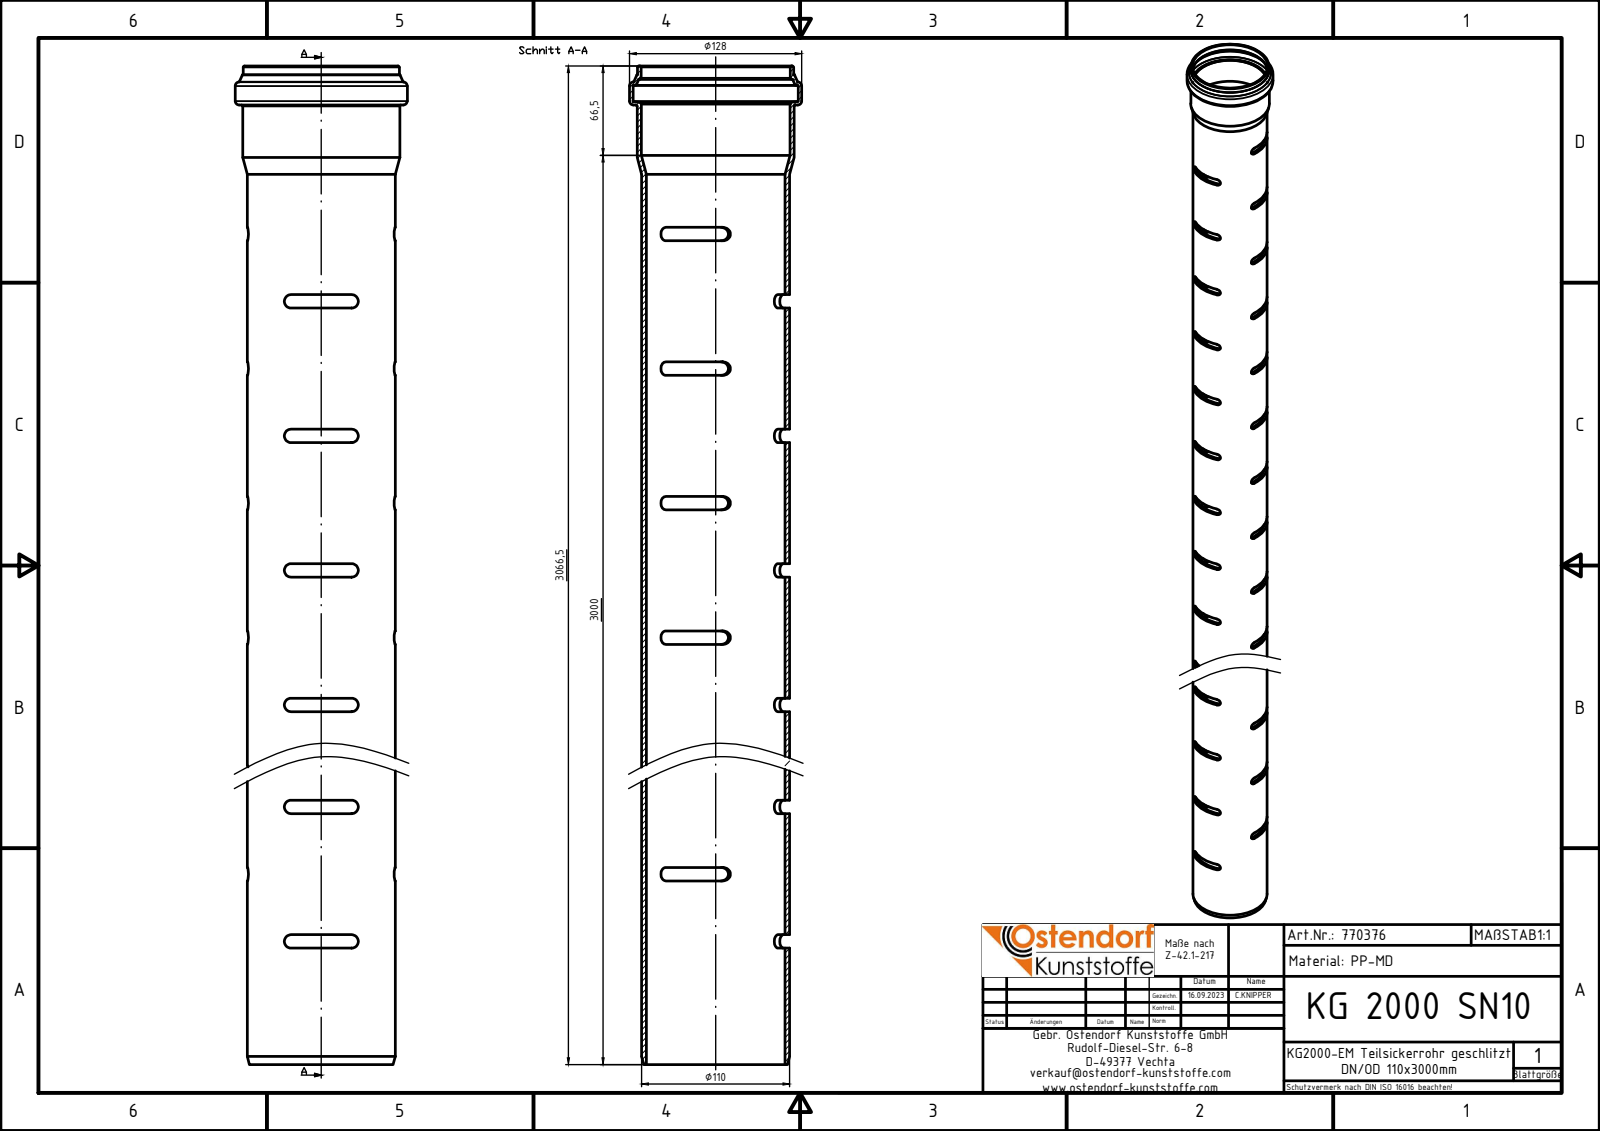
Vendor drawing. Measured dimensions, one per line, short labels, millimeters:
name: 770376z
written by: Autodesk Inventor 2024 (AUTOMOTIVE_DESIGN)
unit: mm
bodies: 1 solid, 384 faces (179 planar, 183 cylindrical, 22 other)
size: 3066.5 × 128 × 128
volume: 3 440 000 mm³; area: 2 007 000 mm²
holes: 1× ⌀102.96, 1× ⌀110.5, 1× ⌀110.9, 1× ⌀122.8
bosses: 1× ⌀128, 1× ⌀116.7, 1× ⌀116.1, 1× ⌀110
rounds: 174× R5
face distances: 100, 200, 300, 400, 500, 600, 700, 800, 900, 1000
